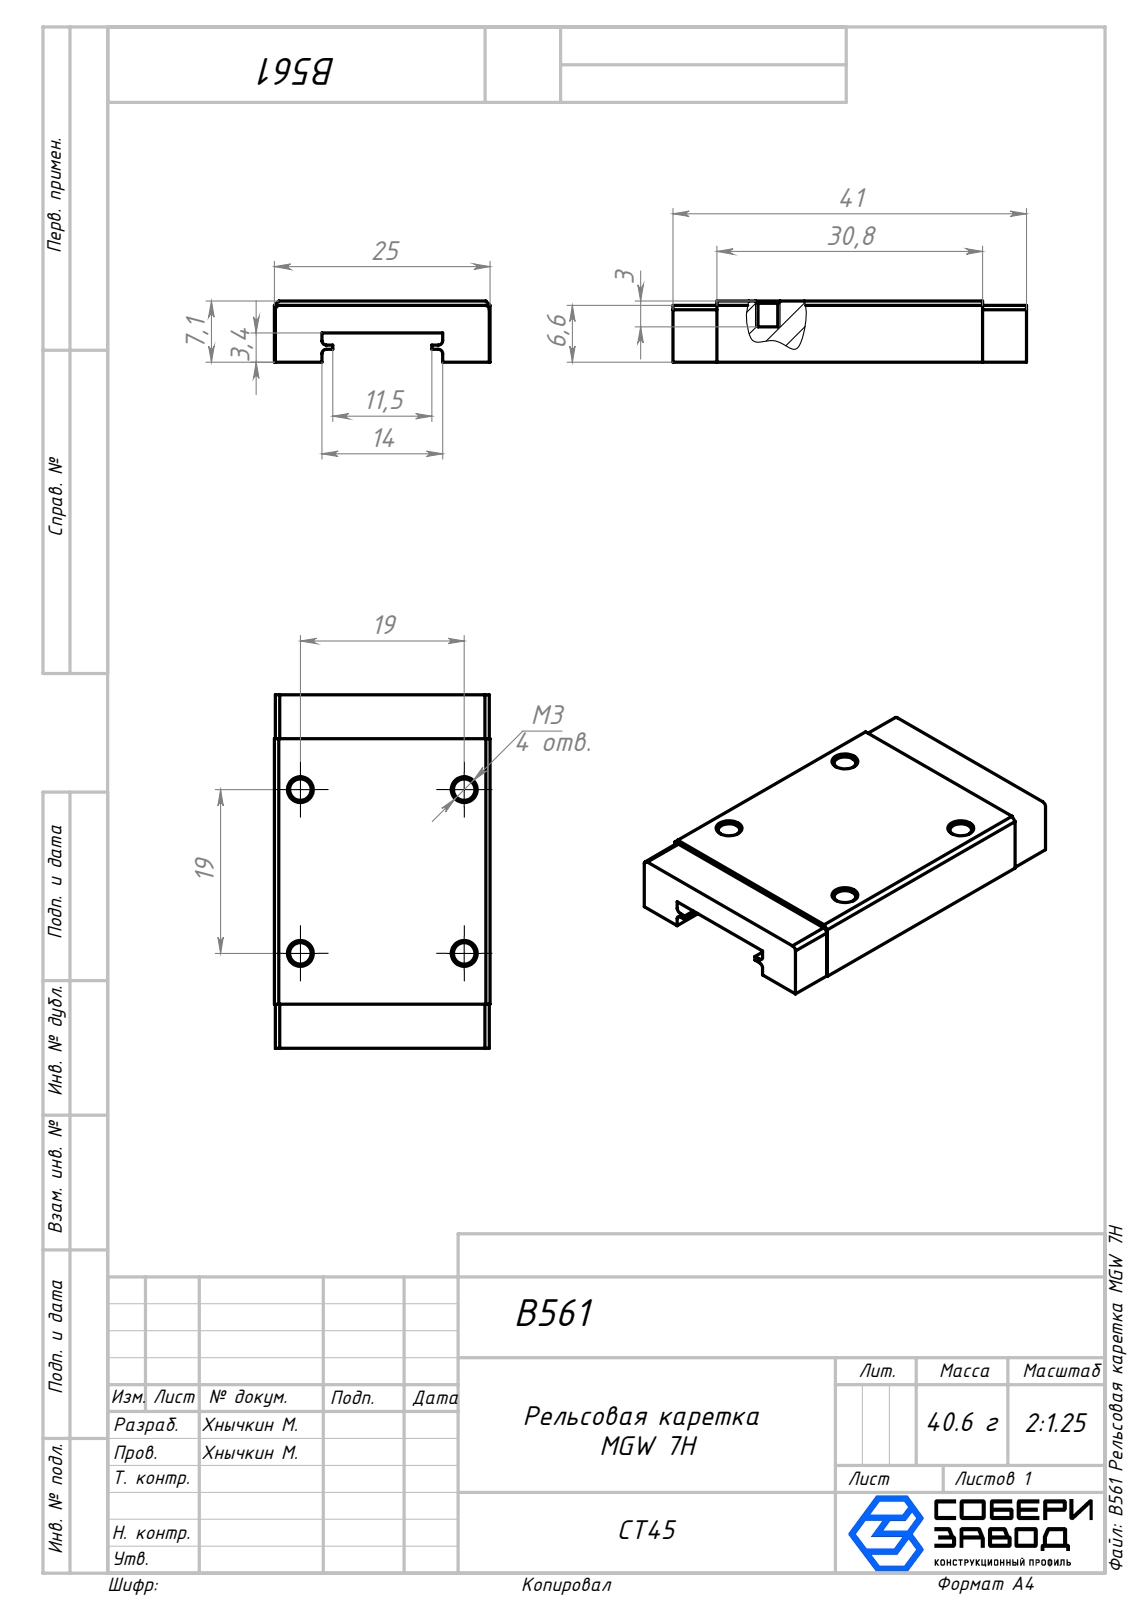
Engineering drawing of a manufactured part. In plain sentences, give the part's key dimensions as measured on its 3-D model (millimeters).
The part is named "B561 Рельсовая каретка MGW 7H". Its 3-D file was written by "SolidWorks 2026 (AUTOMOTIVE_DESIGN)". It is 1 solid with 56 faces: 32 planar, 16 cylindrical and 8 other. Overall it measures 41 by 25 by 7.1 millimeters. Its volume is 5 176 cubic millimeters and its surface area 3 396 square millimeters. Round holes: 4 of diameter 2.5. Partial cylindrical surfaces (rounded edges, fillets, slot ends): 6 of radius 0.5. The main face-to-face distances are 3.7, 3.4, 7.1, 0.5, 6.6, 3.2, 25, 5.5, 19.5, 5.1. The hole center spacings are 19, 26.87.
